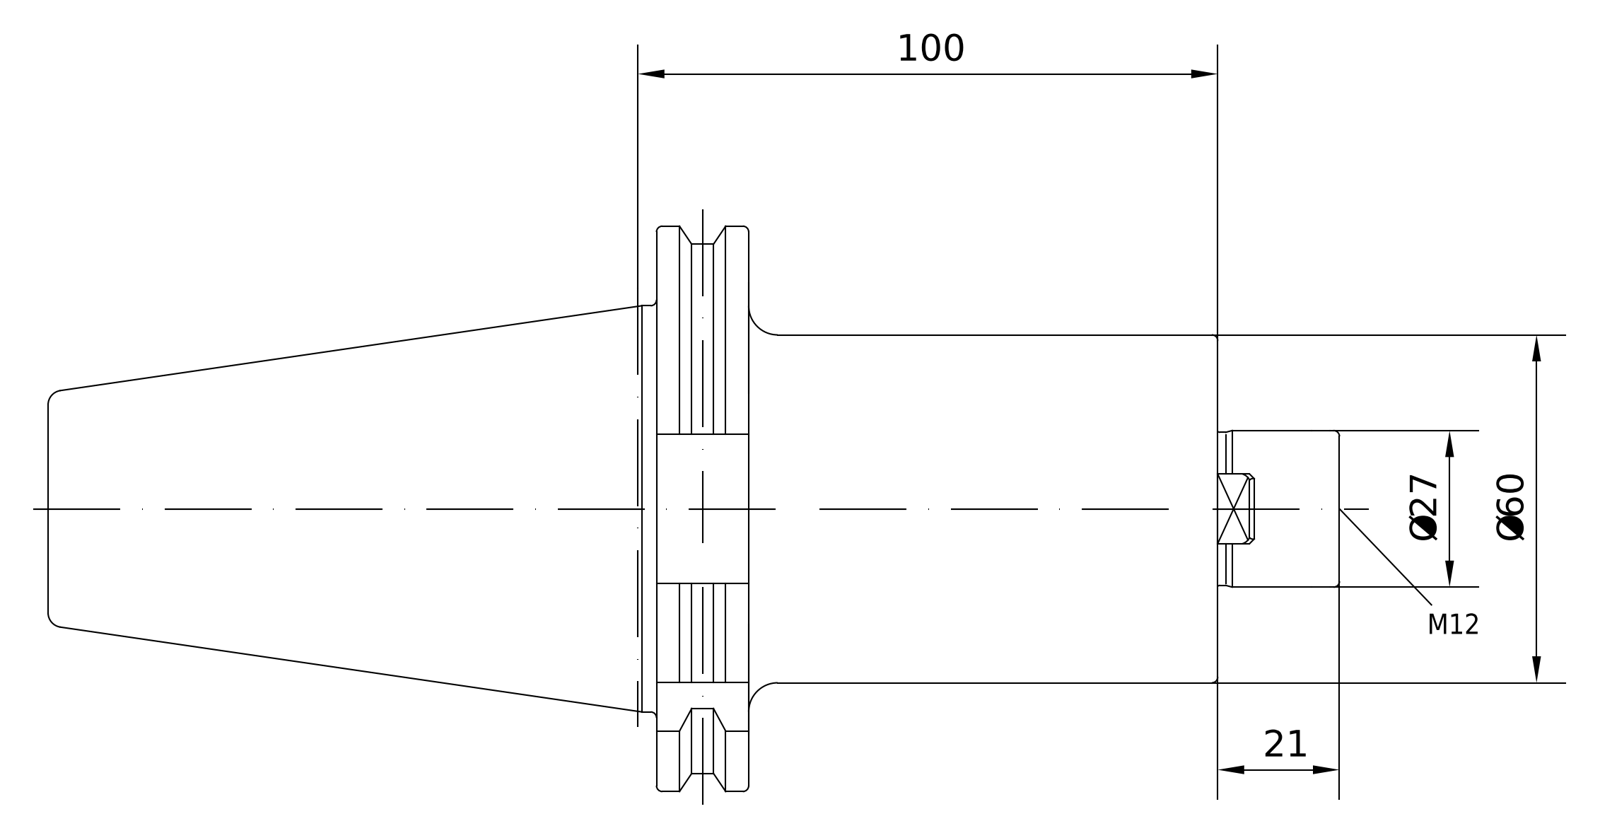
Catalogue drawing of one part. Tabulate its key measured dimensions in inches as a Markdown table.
| quantity | value |
| --- | --- |
| part name | 50-351-27 |
| STEP written by | PRO/ENGINEER BY PARAMETRIC TECHNOLOGY CORPORATION, 2010430 (CONFIG_CONTROL_DESIGN) |
| units | inches |
| bodies | 1 solid, 110 faces (32 planar, 28 cylindrical, 50 other) |
| overall size | 8.764 × 3.837 × 3.701 |
| volume | 35.4 in³ |
| surface area | 95.93 in² |
| round holes (diameter × count) | 0.402 × 1, 0.472 × 1, 0.817 × 1, 0.985 × 1, 1.012 × 1 |
| round bosses / shafts (diameter × count) | 3.583 × 1, 2.722 × 1, 2.362 × 1, 1.063 × 1, 0.945 × 1 |
| partial cylindrical surfaces (radius × count) | 0.069 × 1, 1.919 × 1 |
| main face-to-face distances | 0.624, 3.811, 3.187, 4.638, 4.014, 0.827, 2.866, 4.126, 4.75, 7.937 |
